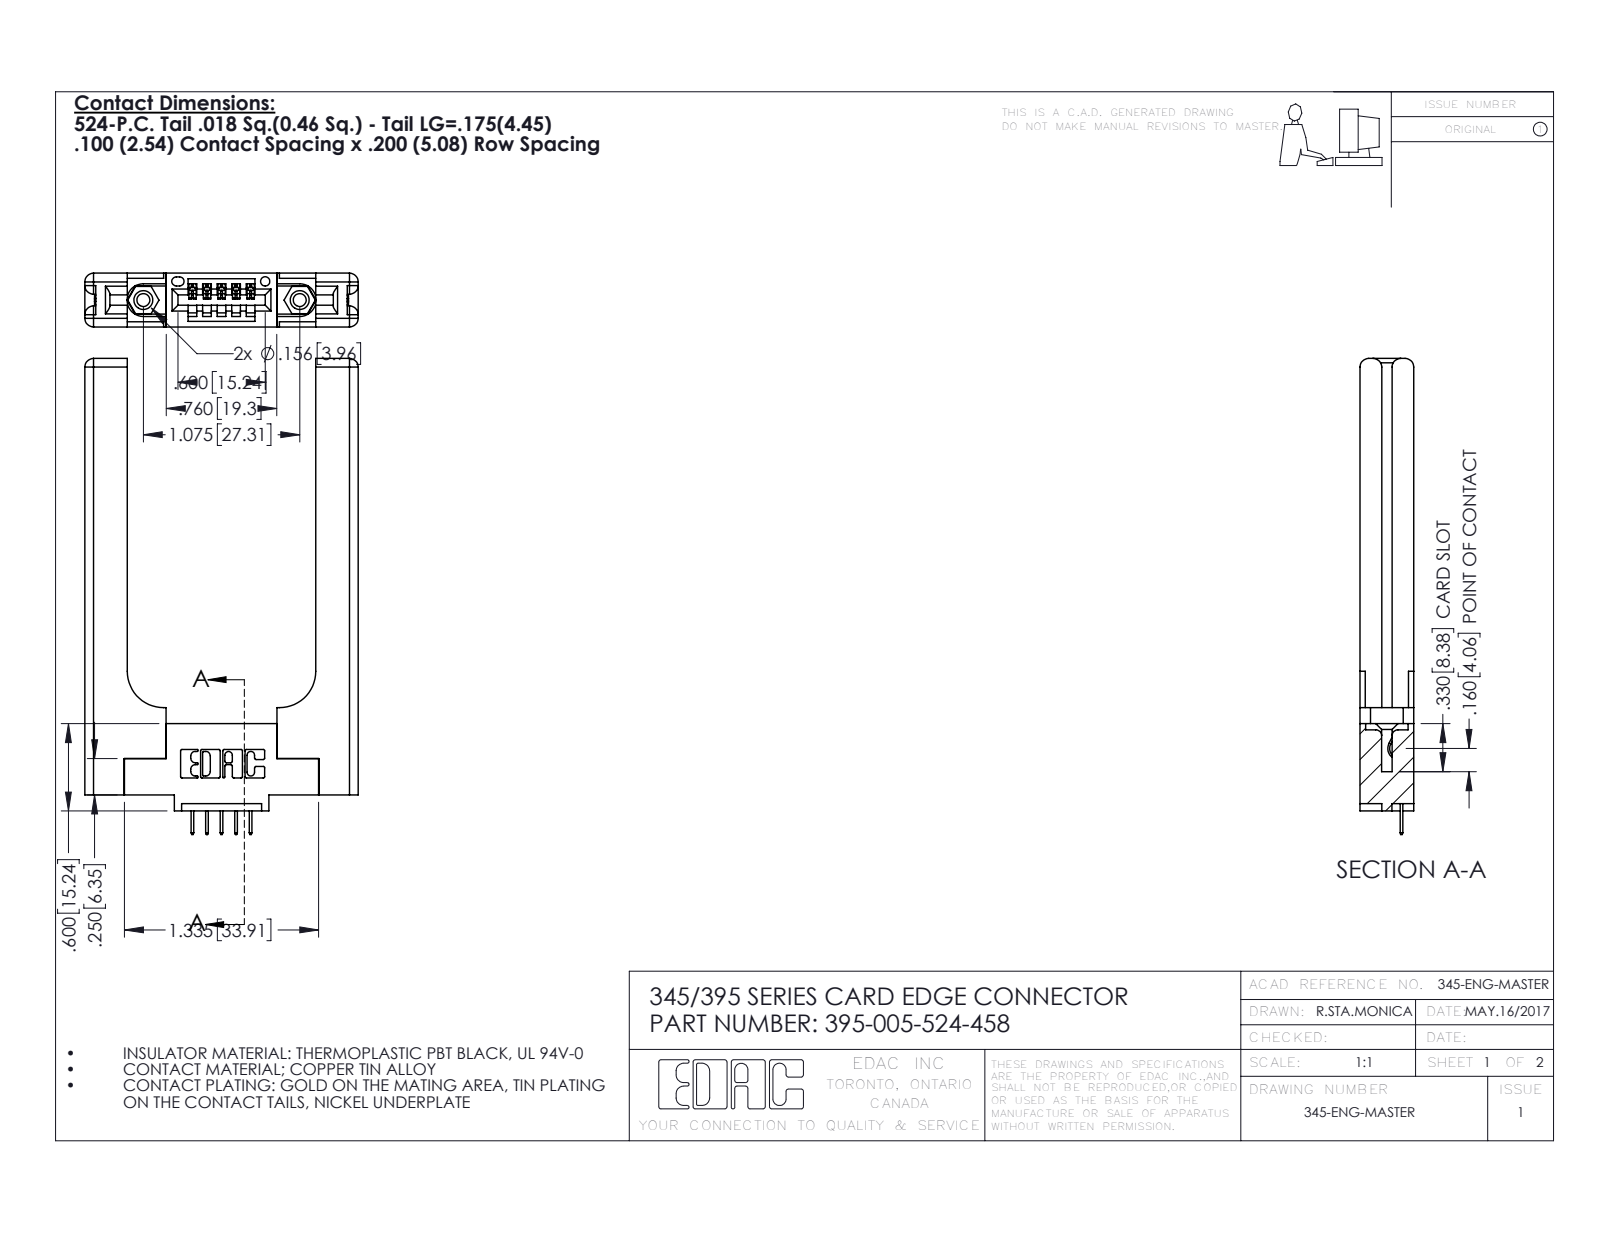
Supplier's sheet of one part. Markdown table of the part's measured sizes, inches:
| quantity | value |
| --- | --- |
| part name | 345-220-058_345-220-058; 345-292-001_345-293-124; 395-005-524-458; 345-250-001_345-250-001-102 (+1 more) |
| STEP written by | SolidWorks 2016 (CONFIG_CONTROL_DESIGN) |
| units | inches |
| bodies | 10 solids, 696 faces (462 planar, 174 cylindrical, 60 other) |
| overall size | 3.272 × 1.879 × 0.37 |
| volume | 0.771 in³ |
| surface area | 15.99 in² |
| round holes (diameter × count) | 0.089 × 2, 0.125 × 2, 0.156 × 2, 0.064 × 1 |
| round bosses / shafts (diameter × count) | 0.155 × 2 |
| partial cylindrical surfaces (radius × count) | 0.01 × 22, 0.06 × 16, 0.006 × 10, 0.007 × 6, 0.031 × 6, 0.026 × 3, 0.03 × 2, 0.031 × 2 |
| main face-to-face distances | 0.37, 0.15, 0.22, 1.296, 0.072, 0.071, 0.148, 0.077, 0.292, 1.587 |
| hole center spacings | 0.27, 0.847, 1.075 |
